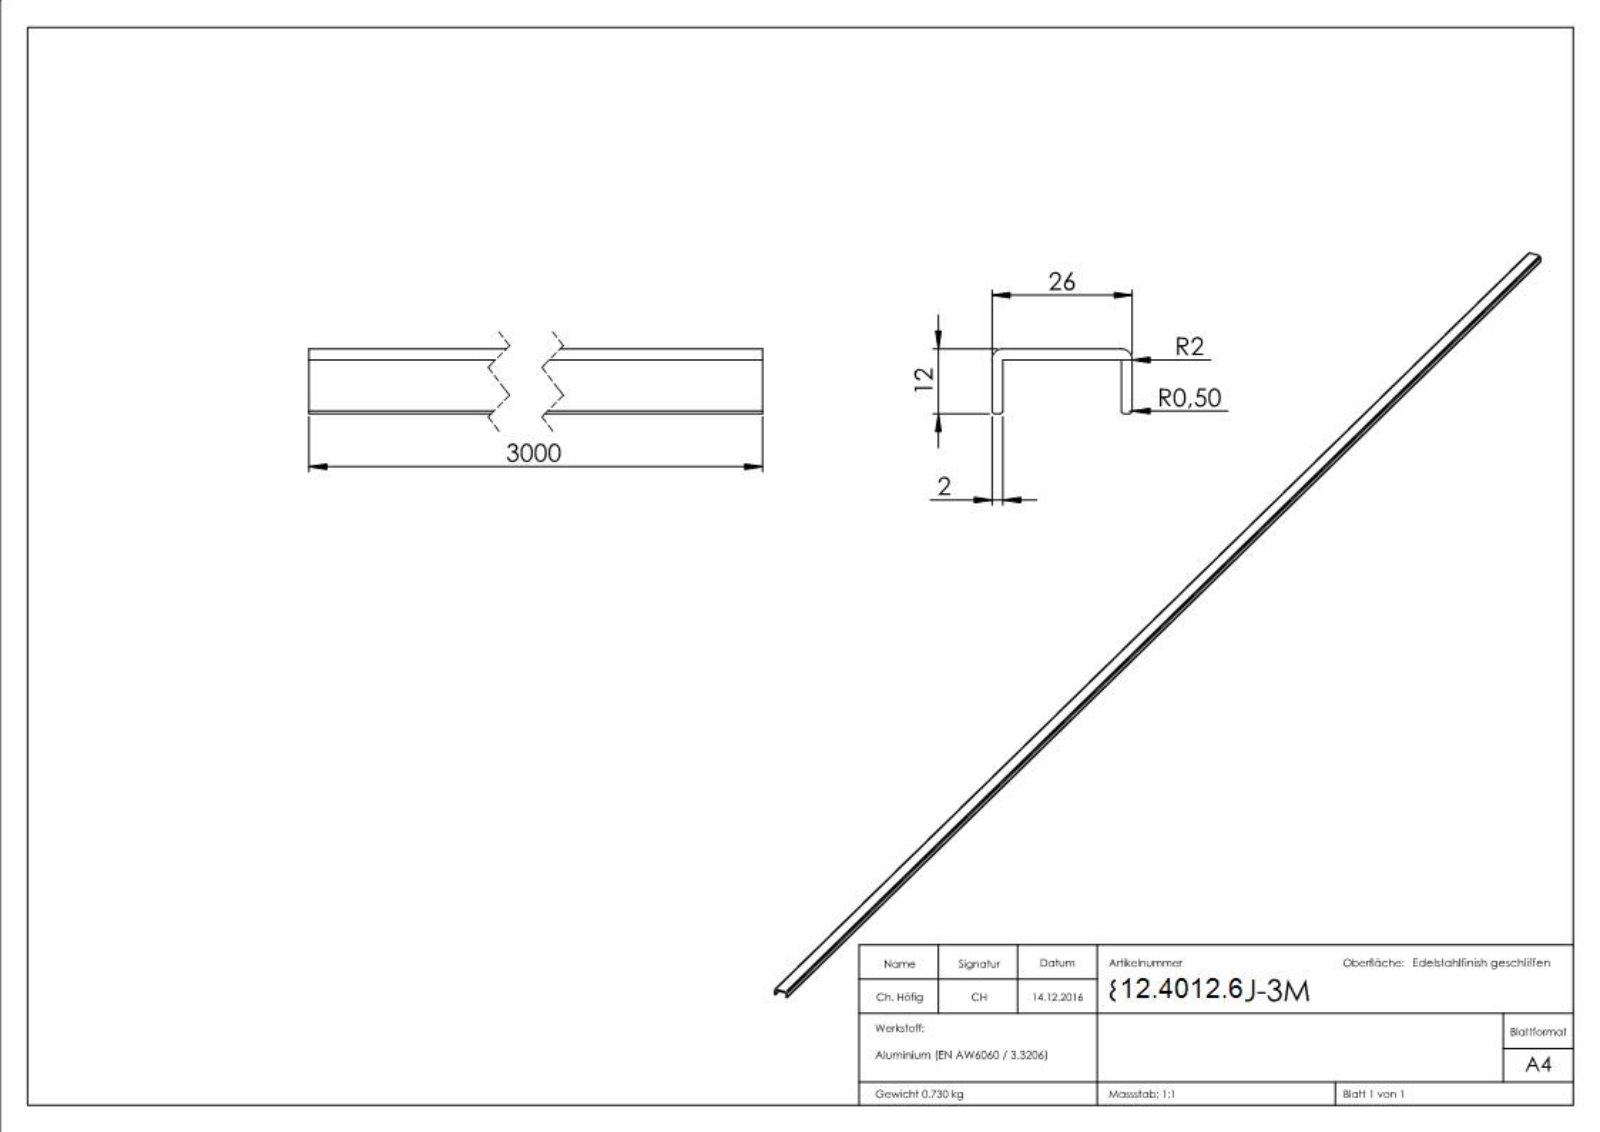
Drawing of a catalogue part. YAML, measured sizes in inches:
part_name: "80537-ALU-3M"
step_written_by: "SolidWorks 2015 (CONFIG_CONTROL_DESIGN)"
units: inches
bodies: {solids: 1, faces: 304, planar: 172, cylindrical: 6, other: 126}
overall_size: [118.11, 1.024, 0.472]
volume: 16.49
surface_area: 434.7
partial_cylinders:
  - {radius: 0.02, count: 4}
  - {radius: 0.079, count: 2}
face_to_face_distances: [0.079, 0.945, 1.024, 0.866, 0.394, 0.472, 118.11, 0.075, 0.87, 0.949]
